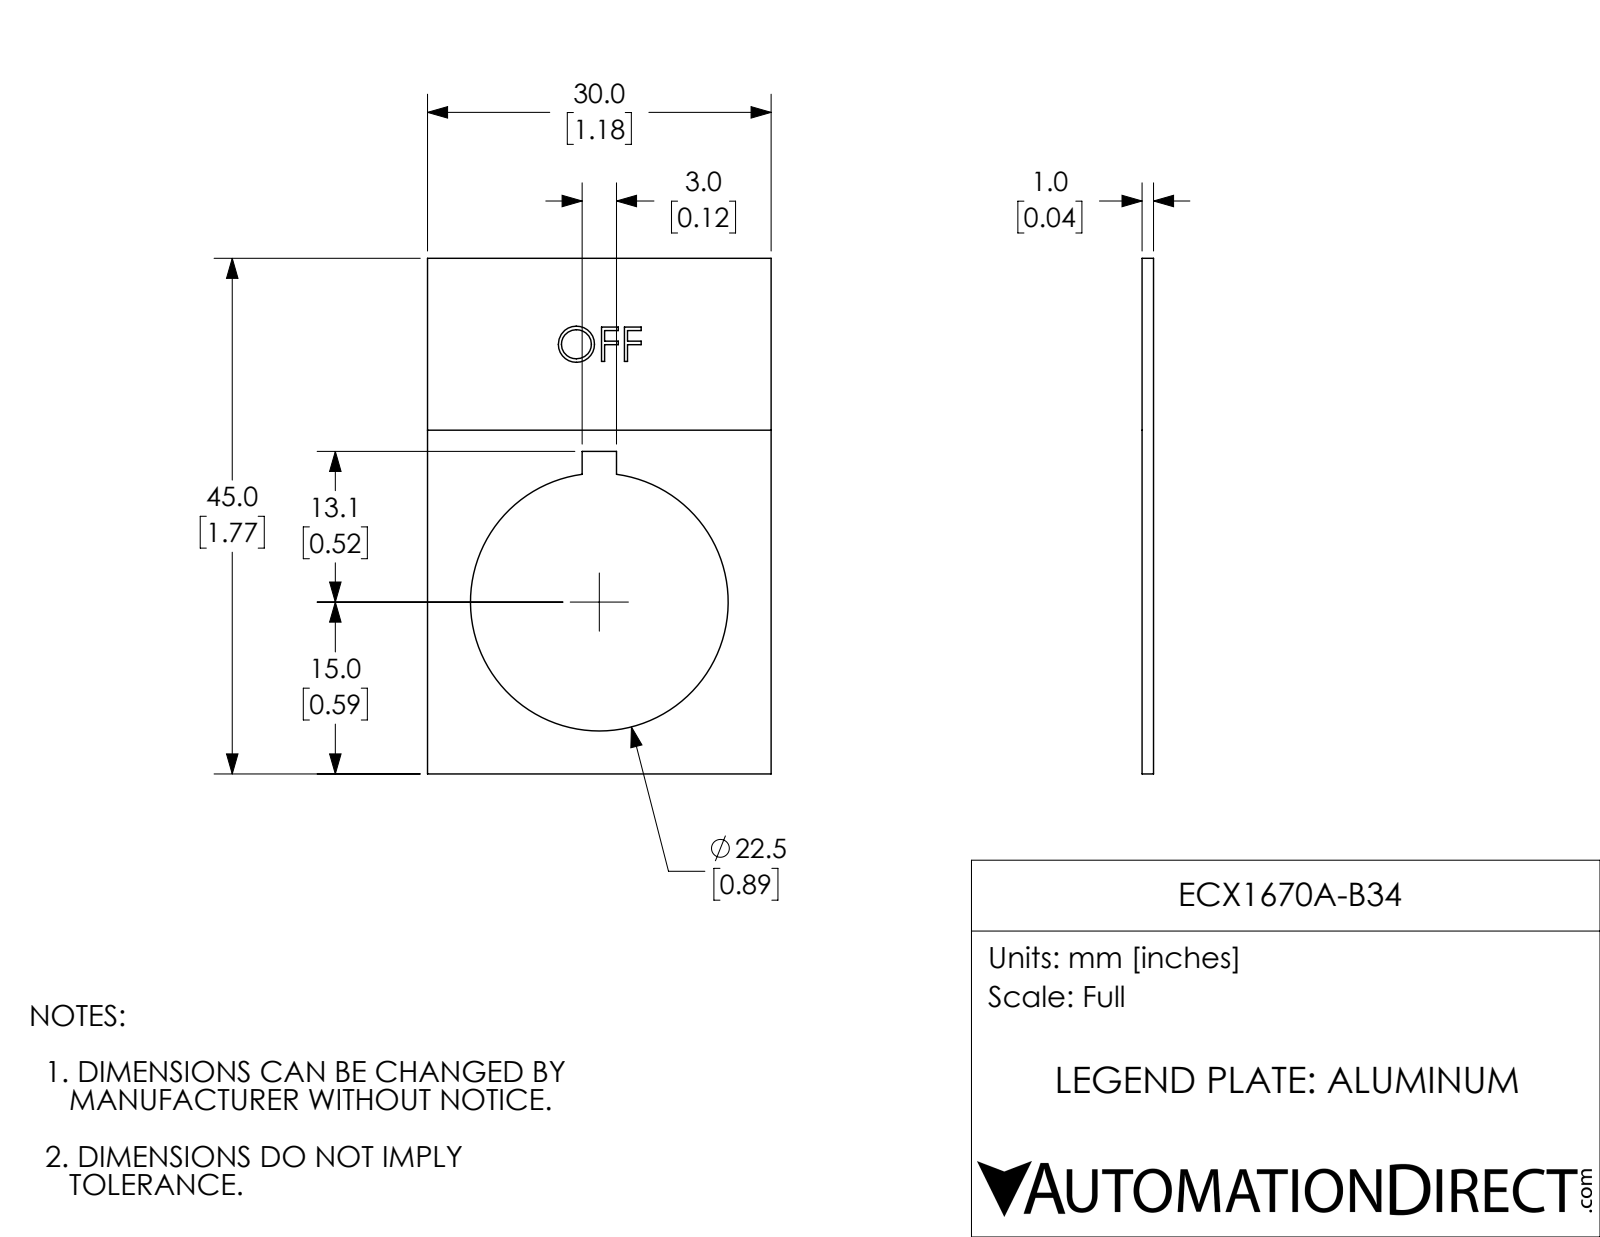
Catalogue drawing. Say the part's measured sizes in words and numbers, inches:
The part is named "ECX1670A-B34". Its 3-D file was written by "SolidWorks 2017 (AUTOMOTIVE_DESIGN)". It is 1 solid with 45 faces: 34 planar, 3 cylindrical and 8 other. Overall it measures 1.772 by 1.181 by 0.039 inches. Its volume is 0.058 cubic inches and its surface area 3.284 square inches. Round holes: 1 of diameter 0.886. The main face-to-face distances are 0.039, 1.181, 1.772, 0.038, 0.531, 0.65, 1.108, 0.663, 0.118, 0.079.
